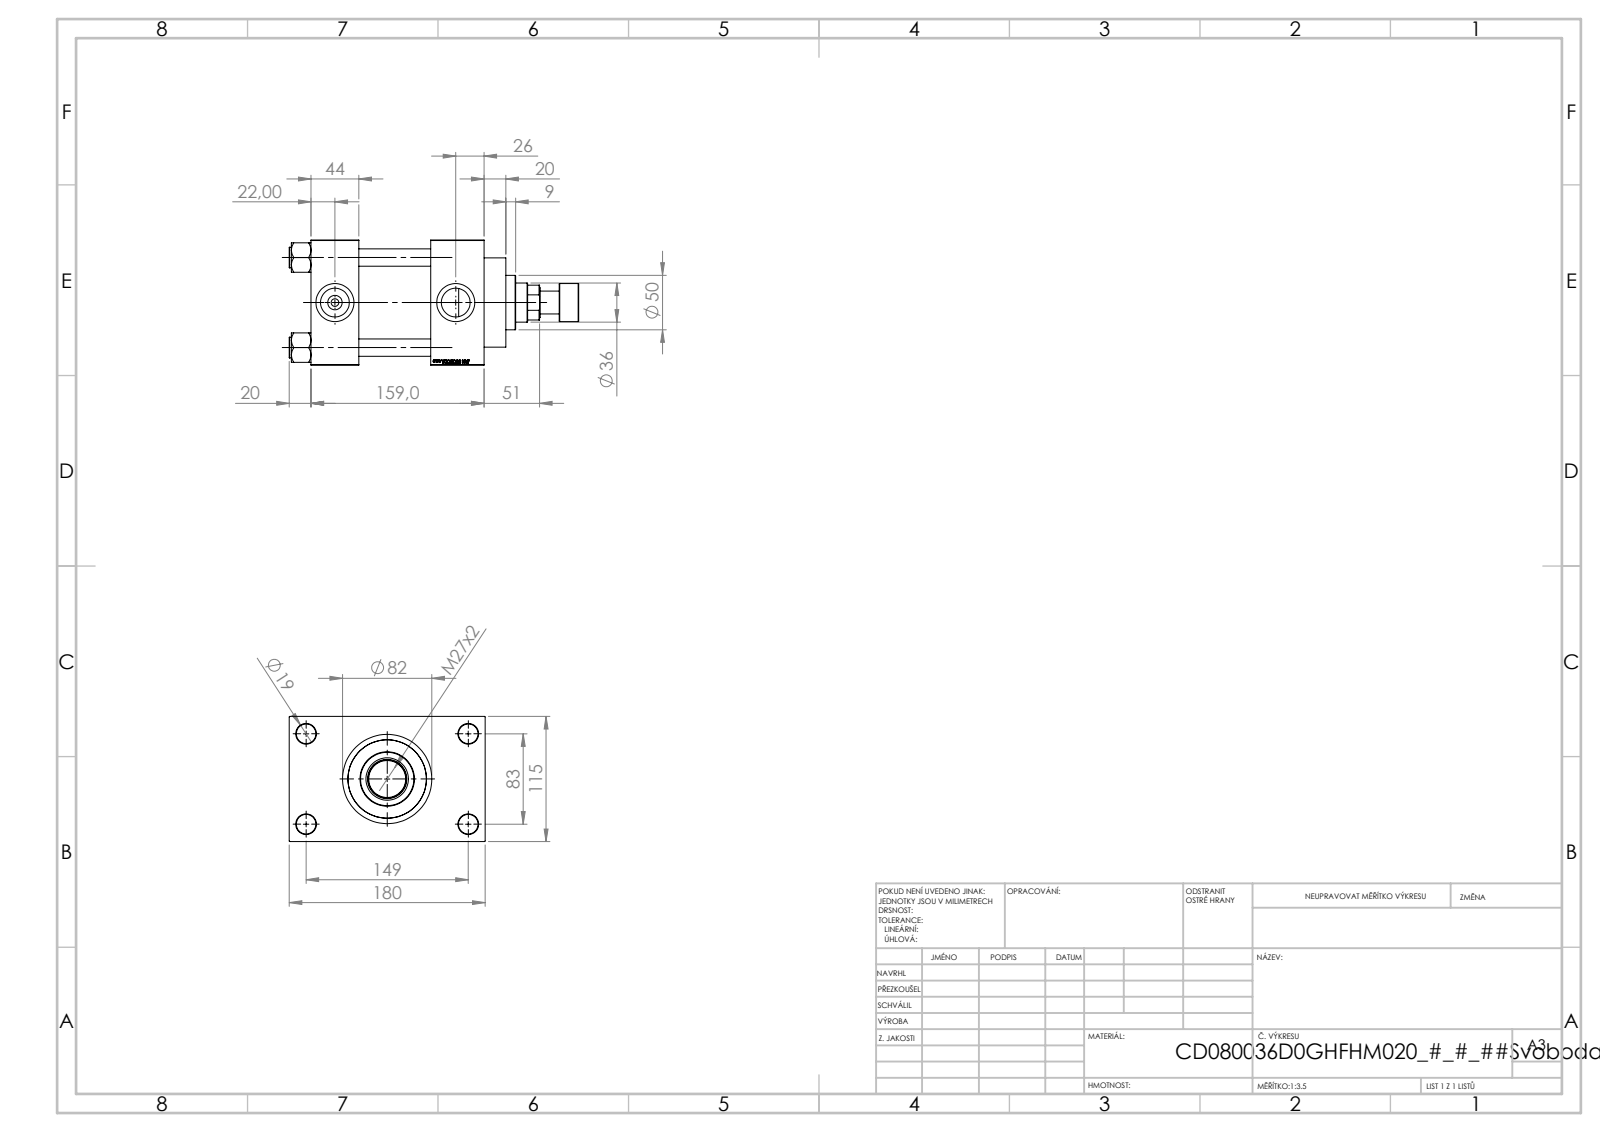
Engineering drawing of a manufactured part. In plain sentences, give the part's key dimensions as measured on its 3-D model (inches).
The part is named "V215CD_D_Body; V215CR_ROD_END_F; V215CD_D_TYCINKA; V215CD_VCP_D (+2 more)". Its 3-D file was written by "SolidWorks 2019 (CONFIG_CONTROL_DESIGN)". It is 12 solids with 1165 faces: 549 planar, 92 cylindrical and 524 other. Overall it measures 10.472 by 7.087 by 4.528 inches. Its volume is 122.2 cubic inches and its surface area 468.4 square inches. Round holes: 4 of diameter 0.63, 4 of diameter 0.709, 2 of diameter 0.276, 2 of diameter 1.041, 2 of diameter 1.378, 1 of diameter 1.004, 1 of diameter 1.417, 1 of diameter 1.535, 1 of diameter 2.402, 1 of diameter 2.835, 1 of diameter 3.15. Round bosses or shafts: 4 of diameter 0.748, 1 of diameter 3.386, 1 of diameter 3.228, 1 of diameter 1.969, 1 of diameter 1.378, 1 of diameter 0.827. The main face-to-face distances are 4.528, 2.598, 1.929, 4.331, 1.732, 6.26, 1.28, 5.807, 0.787, 2.717. The hole center spacings are 1.305, 2.302, 3.256, 3.357, 3.513, 4.561, 5.607, 3.268.
